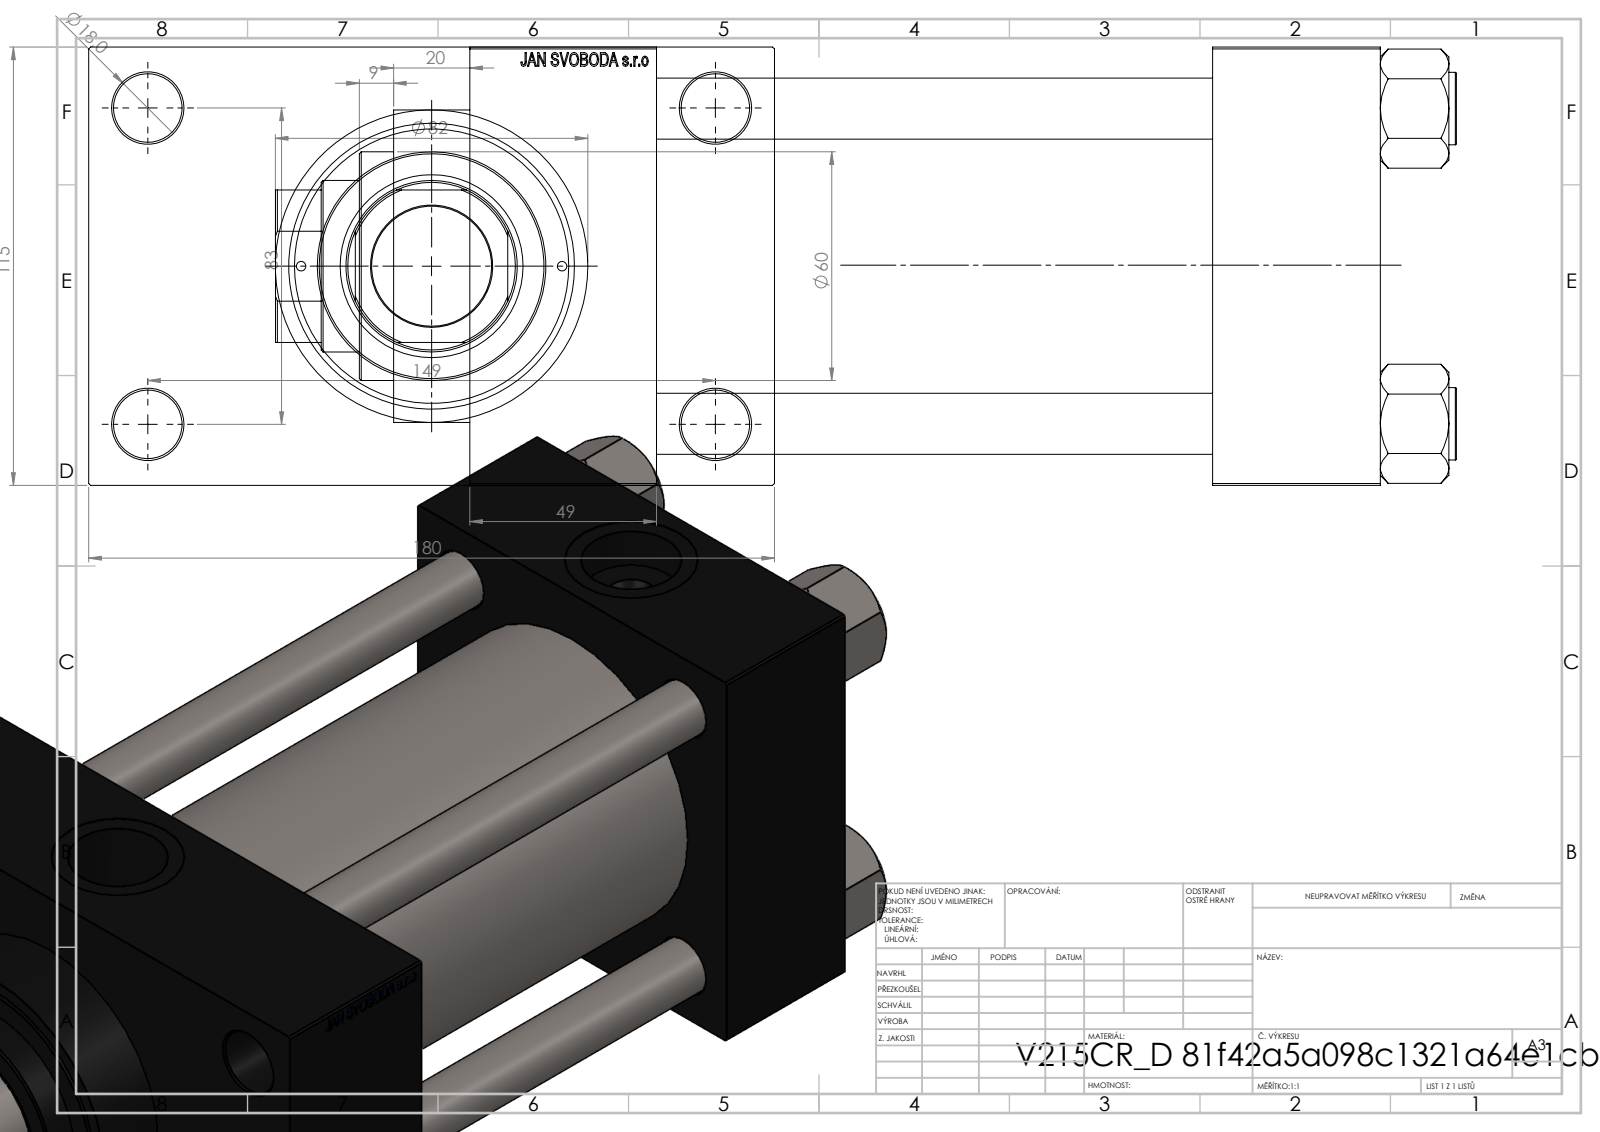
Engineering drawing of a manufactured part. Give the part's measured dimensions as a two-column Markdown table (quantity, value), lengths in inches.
| quantity | value |
| --- | --- |
| part name | V215CR_VCP_D; V215CR_D_TYCINKA; NUT_M5_D; V215CR_D_Body (+1 more) |
| STEP written by | SolidWorks 2019 (CONFIG_CONTROL_DESIGN) |
| units | inches |
| bodies | 11 solids, 1160 faces (547 planar, 93 cylindrical, 520 other) |
| overall size | 12.205 × 7.087 × 4.528 |
| volume | 138.9 in³ |
| surface area | 571.6 in² |
| round holes (diameter × count) | 0.63 × 4, 0.709 × 4, 0.098 × 2, 0.276 × 2, 1.041 × 2, 1.378 × 2, 1.24 × 1, 1.772 × 1, 1.89 × 1, 2.402 × 1, 2.835 × 1, 3.15 × 1 |
| round bosses / shafts (diameter × count) | 0.748 × 4, 3.386 × 1, 3.228 × 1, 2.362 × 1 |
| partial cylindrical surfaces (radius × count) | 0.866 × 1 |
| main face-to-face distances | 4.528, 5.748, 7.677, 1.929, 1.732, 7.48, 9.409, 1.28, 5.807, 7.087 |
| hole center spacings | 1.305, 1.652, 2.276, 2.302, 3.256, 3.357, 3.393, 3.513 |
